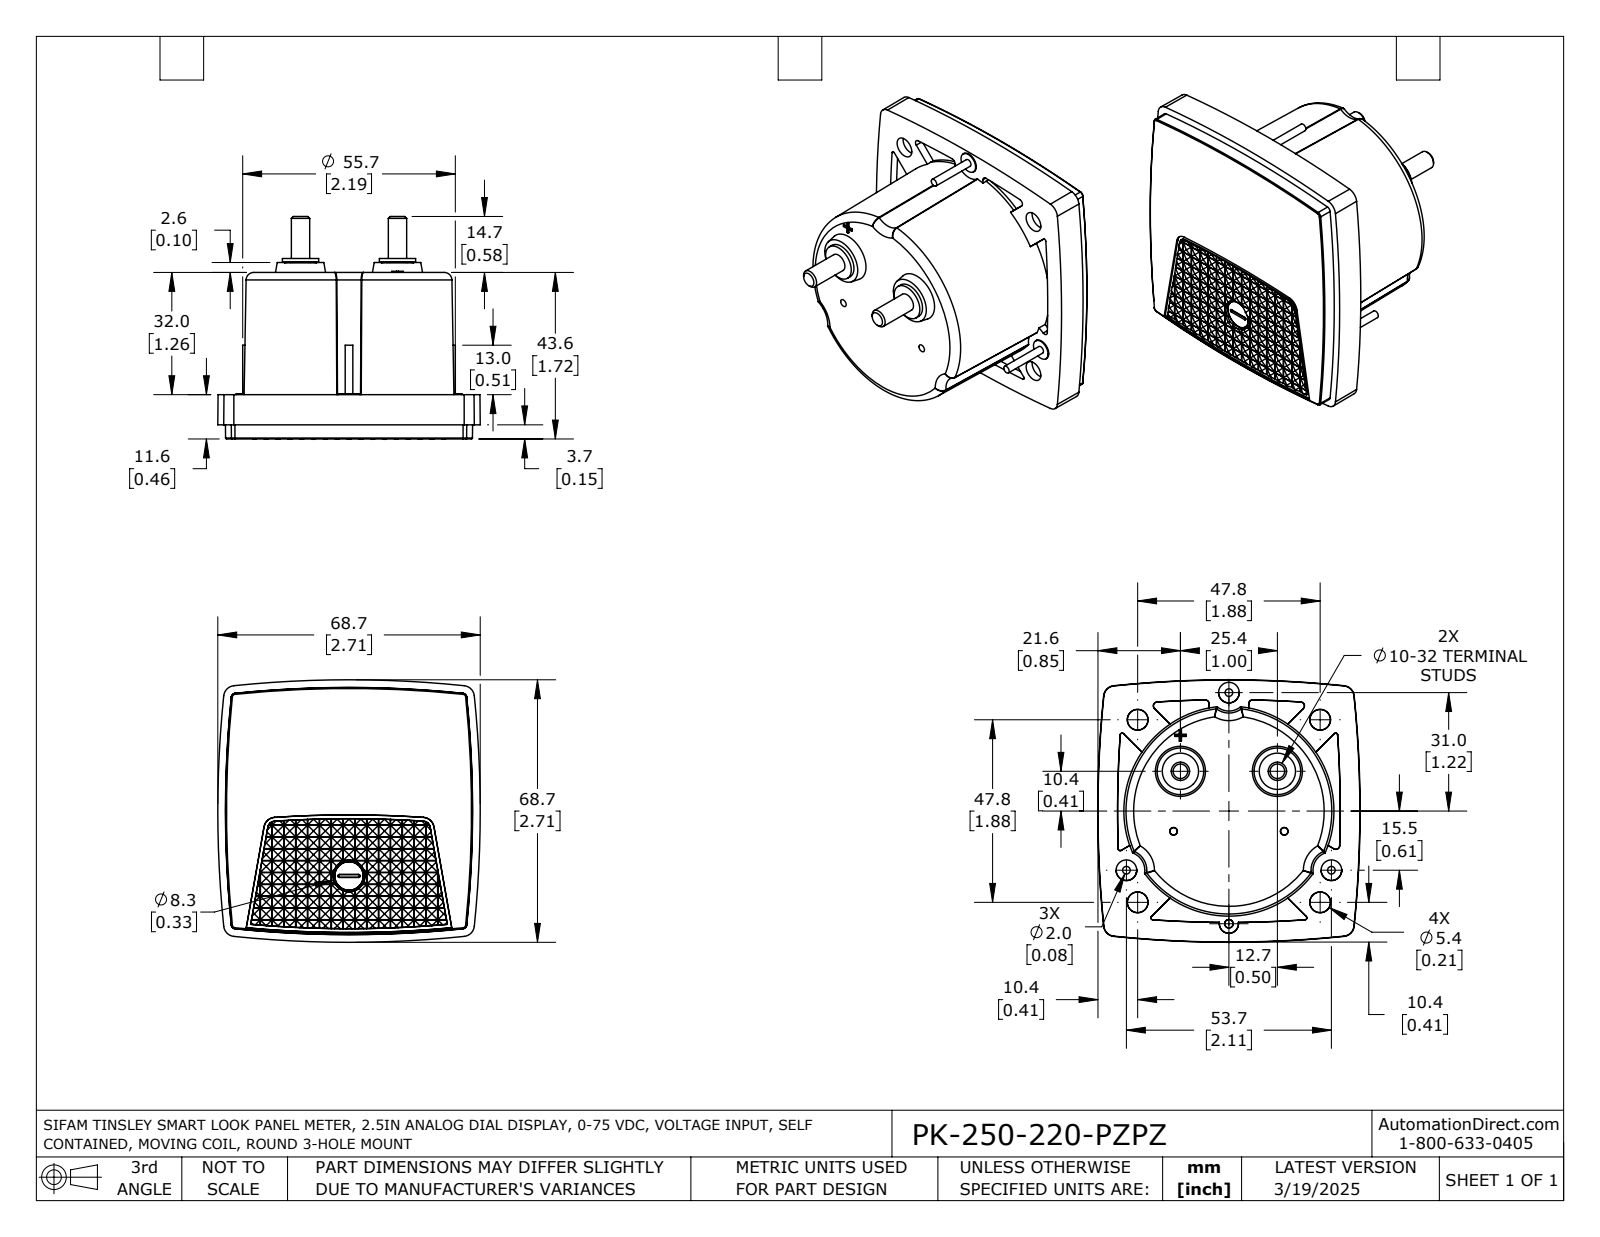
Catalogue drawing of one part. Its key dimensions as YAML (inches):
part_name: "PK-250-220-PZPZ"
step_written_by: "SolidWorks 2021 (AUTOMOTIVE_DESIGN)"
units: inches
bodies: {solids: 1, faces: 1550, planar: 1165, cylindrical: 265, other: 120}
overall_size: [2.706, 2.706, 2.297]
volume: 7.594
surface_area: 30.41
round_bosses_or_shafts:
  - {diameter: 0.213, count: 3}
  - {diameter: 0.079, count: 3}
  - {diameter: 0.374, count: 2}
  - {diameter: 0.189, count: 2}
  - {diameter: 0.215, count: 1}
partial_cylinders:
  - {radius: 0.167, count: 2}
  - {radius: 1.083, count: 1}
face_to_face_distances: [1.717, 1.26, 0.457, 0.024, 0.087, 0.096, 0.311, 0.12, 0.072, 1.346]
